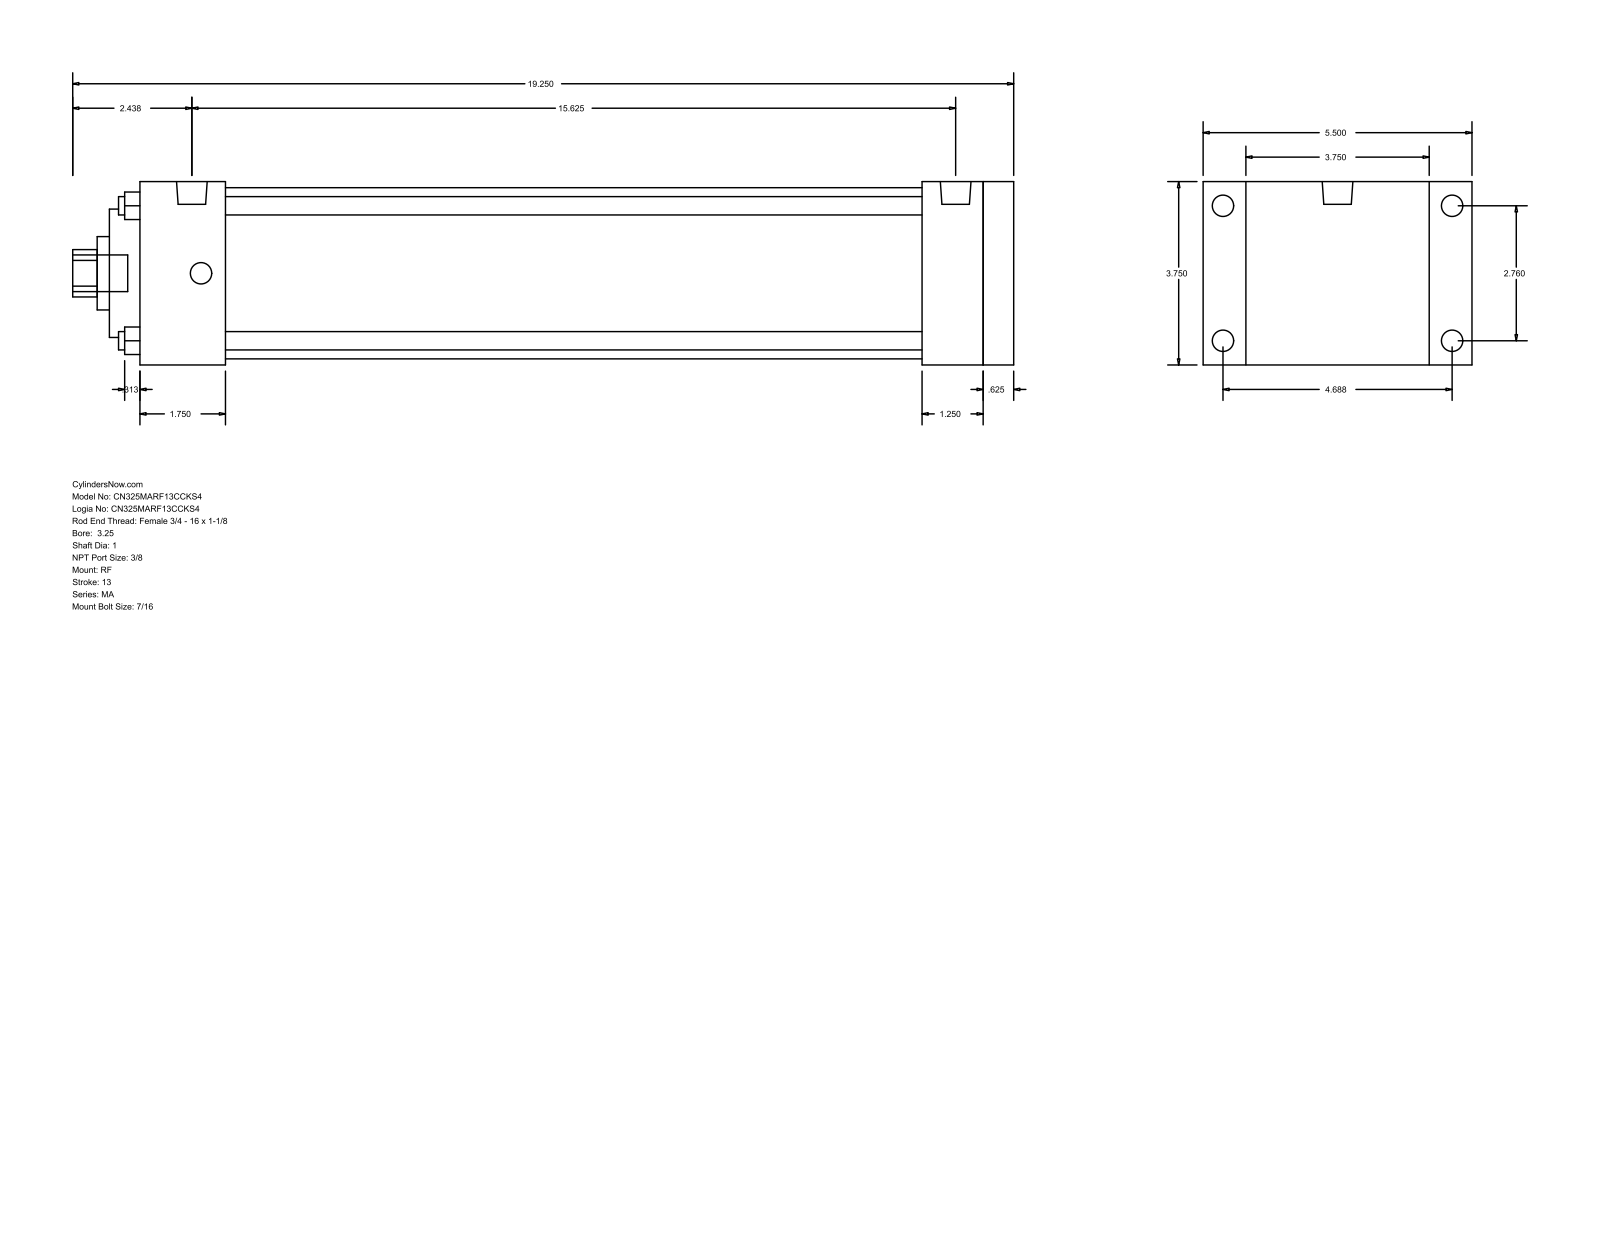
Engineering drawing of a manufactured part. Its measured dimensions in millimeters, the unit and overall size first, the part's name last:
Units: millimetres
Overall size (bounding box): 488.95 × 139.7 × 95.25
Round holes (diameter × count): ⌀9.53 ×4, ⌀25.4 ×1, ⌀38.1 ×1, ⌀66.67 ×1, ⌀88.9 ×1
Round bosses / shafts (diameter × count): ⌀11.11 ×8, ⌀15.93 ×2, ⌀19.05 ×1
Partial cylindrical surfaces — rounded edges, fillets, slot ends (radius × count): R12.29 ×1
Main face-to-face distances: 95.24, 454.03, 438.15, 15.88, 22.23, 117.47, 15.87, 406.4, 31.75, 47.63
Hole centre spacings: 49.57, 70.1, 99.14
Bodies: 0 solids, 94 faces (65 planar, 29 cylindrical, 0 other)
Part name (STEP PRODUCT): MA_RF__0325_1
STEP written by: GSSL Pune (CONFIG_CONTROL_DESIGN)
